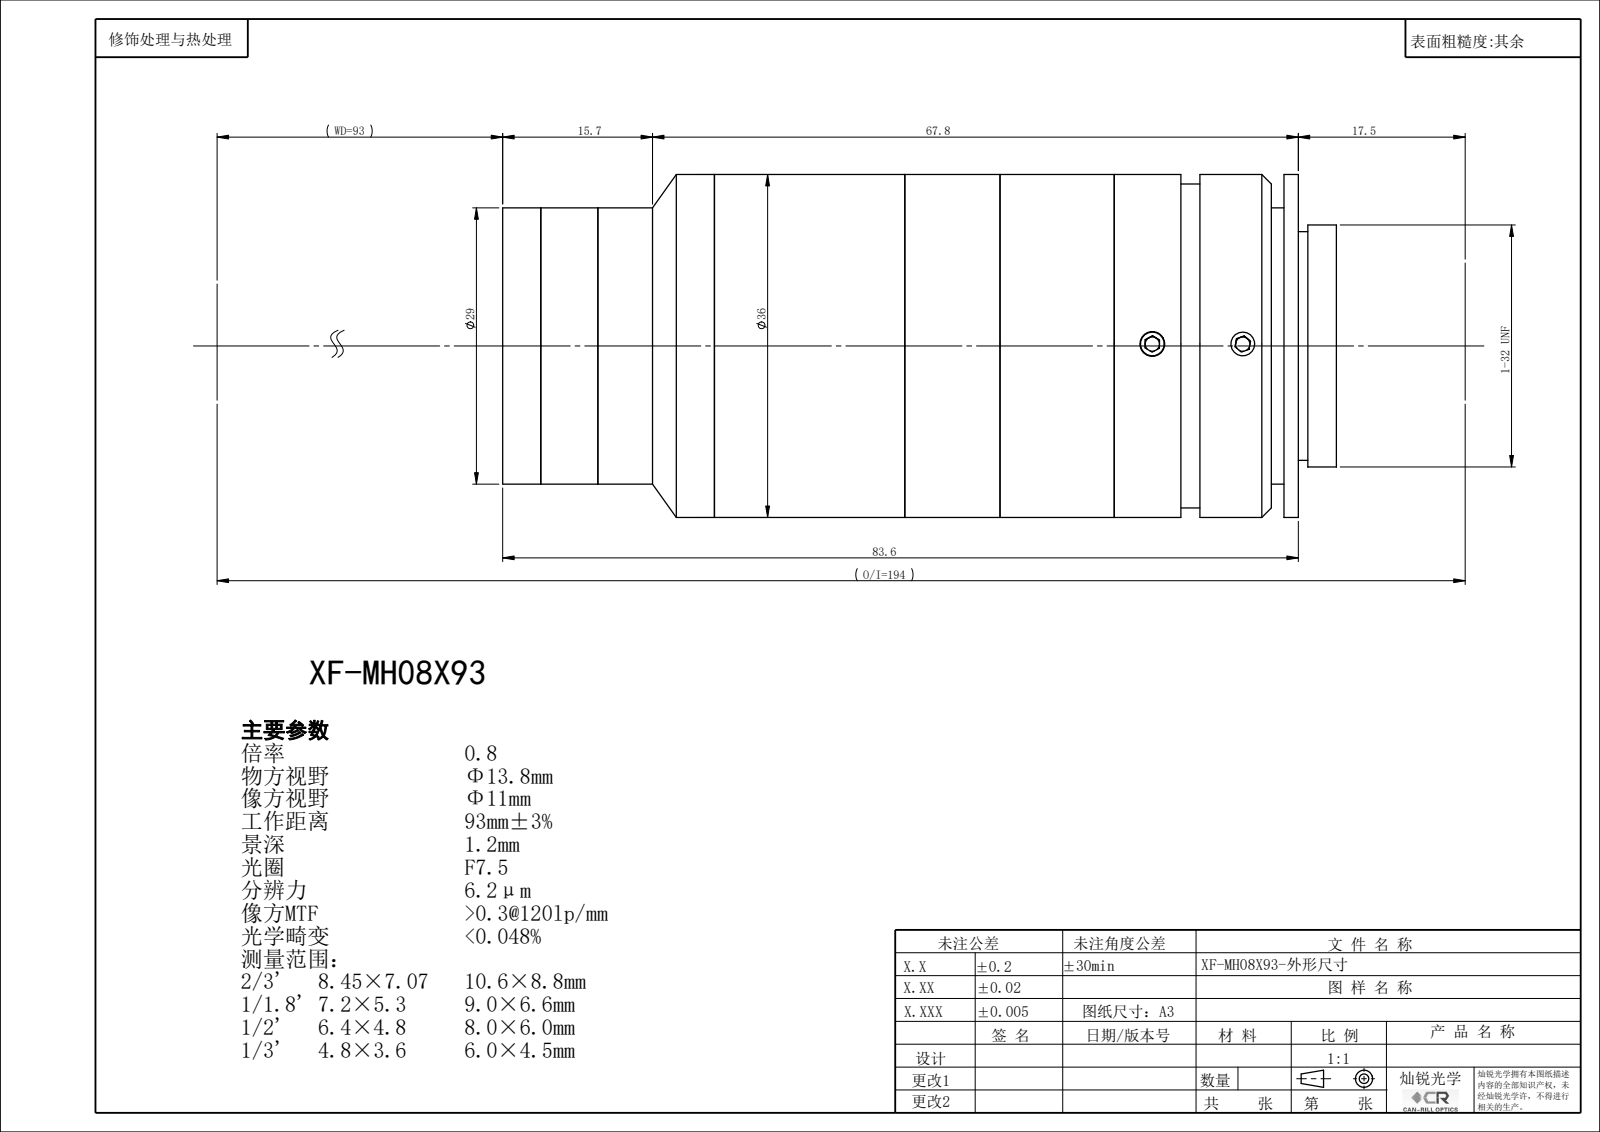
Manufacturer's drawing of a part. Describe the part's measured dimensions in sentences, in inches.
The part is named "XF-MH08X93". Its 3-D file was written by "SolidWorks 2022 (CONFIG_CONTROL_DESIGN)". It is 0 solids with 132 faces: 66 planar, 44 cylindrical and 22 other. Overall it measures 3.448 by 1.418 by 1.417 inches. Round holes: 3 of diameter 0.098, 1 of diameter 0.551, 1 of diameter 0.882, 1 of diameter 0.945, 1 of diameter 0.98, 1 of diameter 1.024, 1 of diameter 1.039. Round bosses or shafts: 1 of diameter 1.417, 1 of diameter 1.339, 1 of diameter 1.142, 1 of diameter 1. The main face-to-face distances are 3.141, 0.059, 3.081, 0.394, 1.907, 1.174, 1.233, 0.726, 1.181, 2.356.
